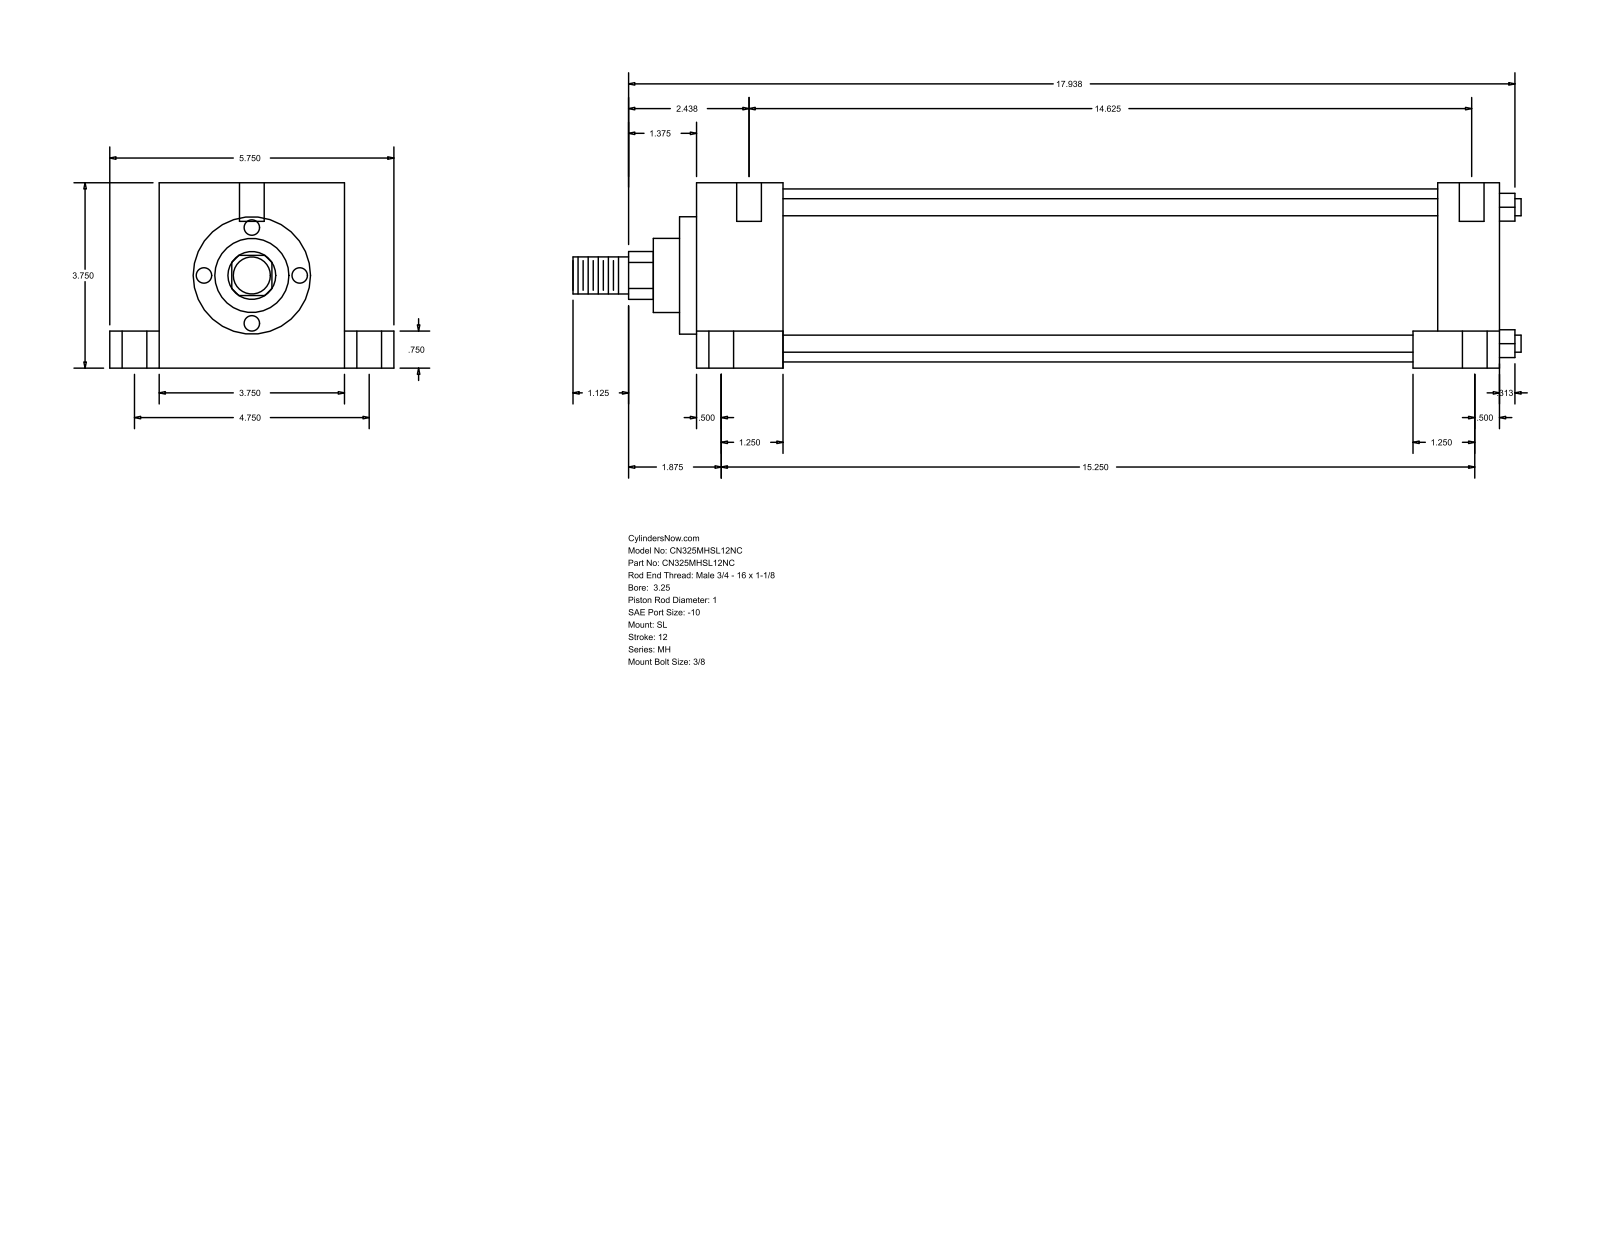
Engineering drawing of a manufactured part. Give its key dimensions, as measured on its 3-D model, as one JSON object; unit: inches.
{"part_name": "MH_SL__0325_1", "step_written_by": "GSSL Pune (CONFIG_CONTROL_DESIGN)", "units": "inches", "bodies": {"solids": 0, "faces": 110, "planar": 77, "cylindrical": 33, "other": 0}, "overall_size": [19.187, 5.75, 3.75], "round_holes": [[0.5, 6], [0.219, 4], [0.75, 4]], "round_bosses_or_shafts": [[0.345, 4], [3.5, 1], [2.375, 1], [1.5, 1], [1, 1], [0.75, 1]], "partial_cylinders_radius": [[0.484, 1]], "face_to_face_distances": [3.75, 16.25, 1.75, 14.5, 1, 4.75, 0.75, 3, 15, 13.25], "hole_center_spacings": [2.376, 2.378, 2.427, 2.441, 4.75, 14.875, 14.879, 14.94]}
